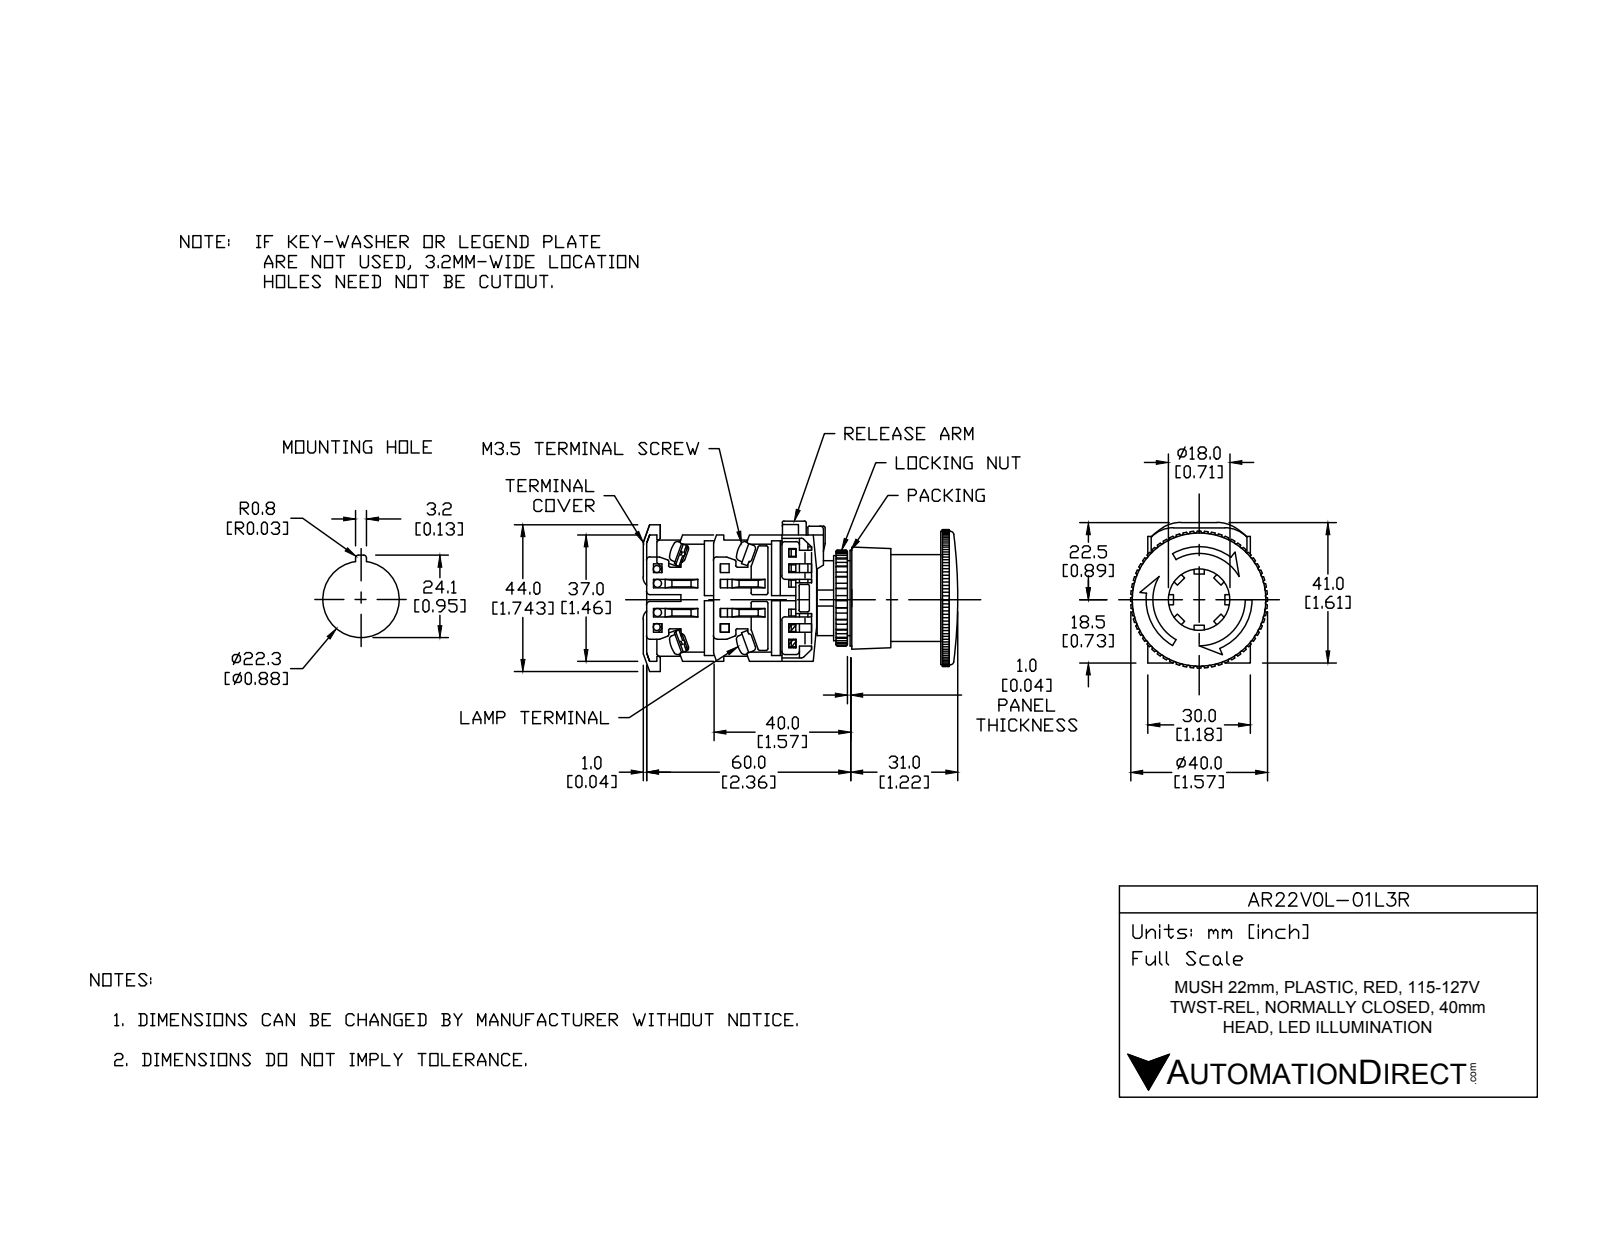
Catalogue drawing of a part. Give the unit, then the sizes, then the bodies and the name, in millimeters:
Units: millimetres
Overall size (bounding box): 92.5 × 43.81 × 39.99
Round holes (diameter × count): ⌀21.8 ×1, ⌀22 ×1, ⌀25.4 ×1
Round bosses / shafts (diameter × count): ⌀5 ×4, ⌀29.8 ×1, ⌀25 ×1, ⌀24 ×1, ⌀21.75 ×1, ⌀17 ×1
Partial cylindrical surfaces — rounded edges, fillets, slot ends (radius × count): R0.5 ×119, R1.75 ×8, R5 ×4, R4 ×2, R13.5 ×1, R15 ×1, R16.59 ×1, R17.59 ×1
Main face-to-face distances: 1, 18, 29, 20, 10, 2, 16, 19, 20.5, 0.35
Volume: 56 208 mm³ · Surface area: 28 267 mm²
Bodies: 17 solids, 725 faces (308 planar, 310 cylindrical, 107 other)
Part name (STEP PRODUCT): AR22V0L-01L3R
STEP written by: SolidWorks 2017 (AUTOMOTIVE_DESIGN)
